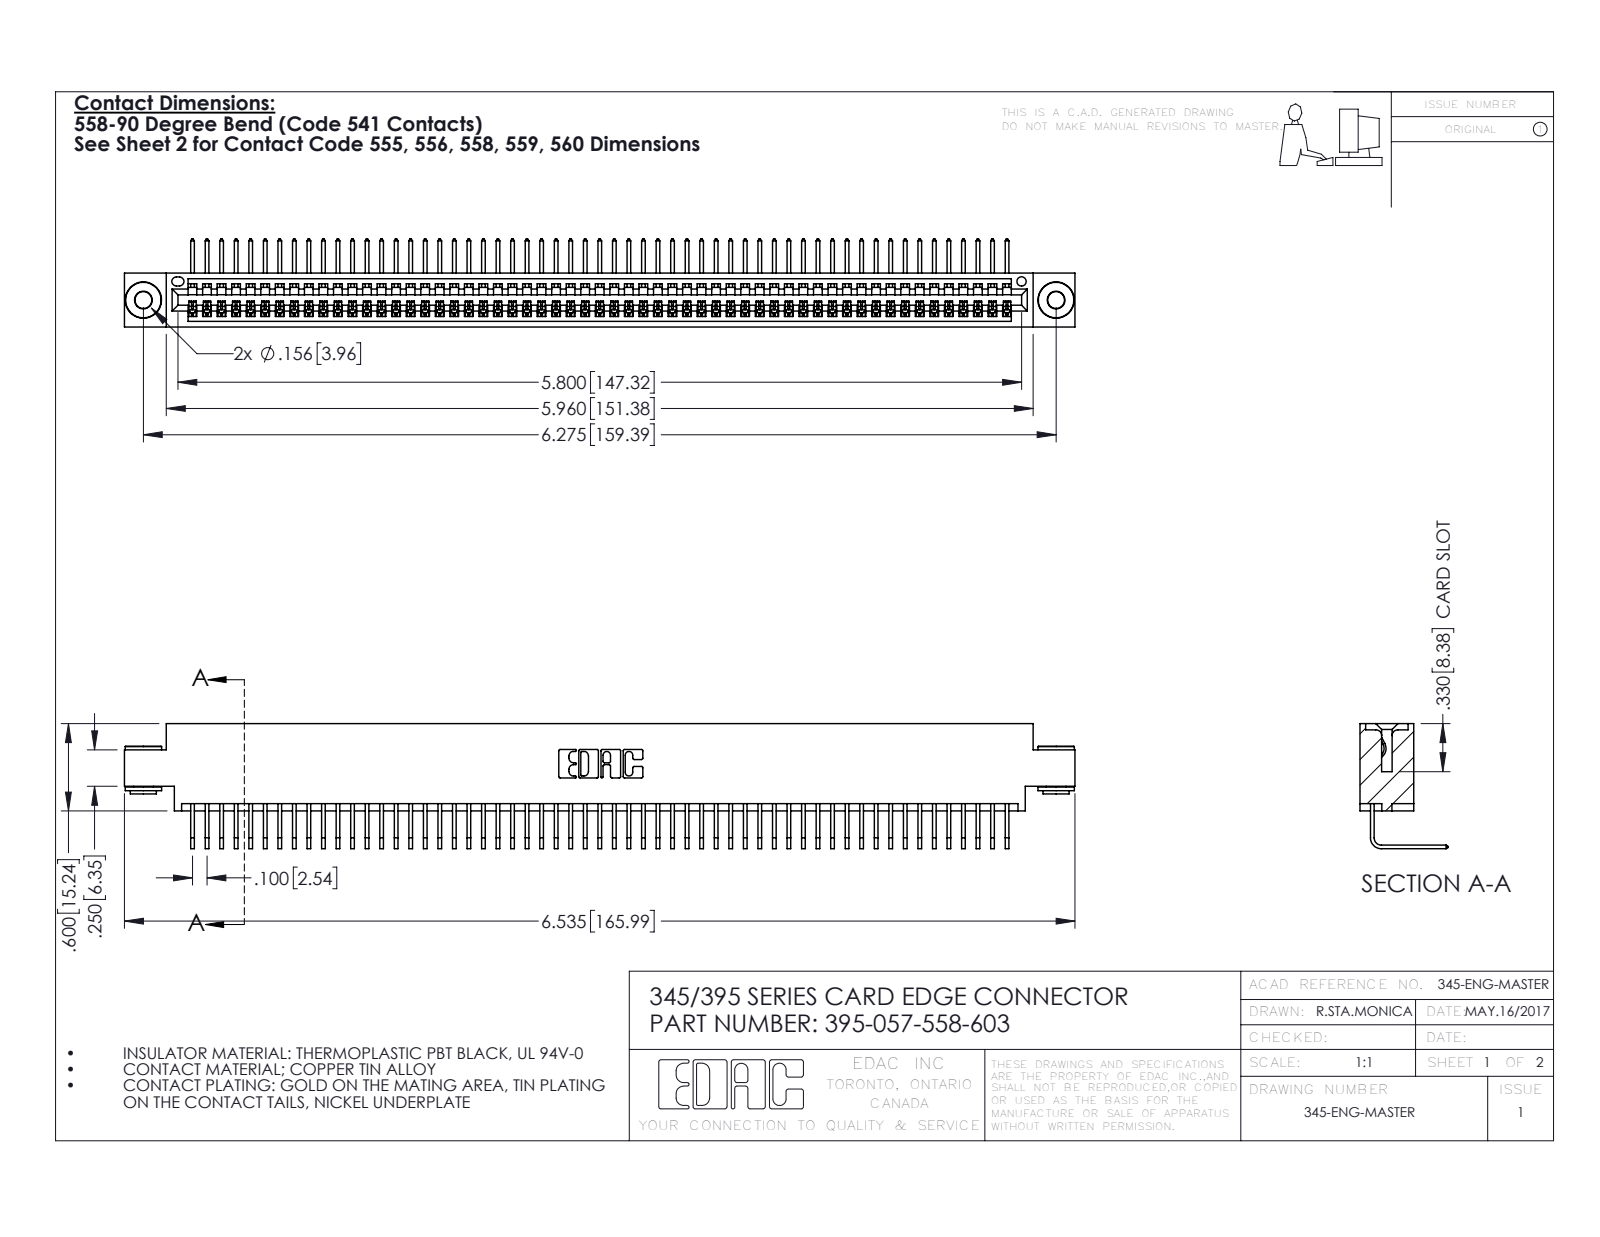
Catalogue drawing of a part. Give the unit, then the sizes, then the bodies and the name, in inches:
Units: inches
Overall size (bounding box): 6.535 × 0.859 × 0.605
Round holes (diameter × count): ⌀0.116 ×2, ⌀0.156 ×2, ⌀0.064 ×1
Round bosses / shafts (diameter × count): ⌀0.25 ×2, ⌀0.18 ×2, ⌀0.136 ×2
Partial cylindrical surfaces — rounded edges, fillets, slot ends (radius × count): R0.006 ×114, R0.01 ×22, R0.007 ×6, R0.031 ×6, R0.026 ×3, R0.031 ×2, R0.04 ×2, R0.014 ×1
Main face-to-face distances: 0.072, 0.298, 0.37, 0.2, 0.098, 0.272, 0.025, 0.225, 0.175, 0.149
Hole centre spacings: 0.27, 6.039, 6.275
Volume: 0.975 in³ · Surface area: 35.5 in²
Bodies: 60 solids, 3588 faces (2488 planar, 1092 cylindrical, 8 other)
Part name (STEP PRODUCT): 395-057-558-603; 345-250-002_345-250-002-102; 345-292-001_558 Tail - 2; 345 Part_0.170 Offset - 0.156 Dia-TH
STEP written by: SolidWorks 2016 (CONFIG_CONTROL_DESIGN)
